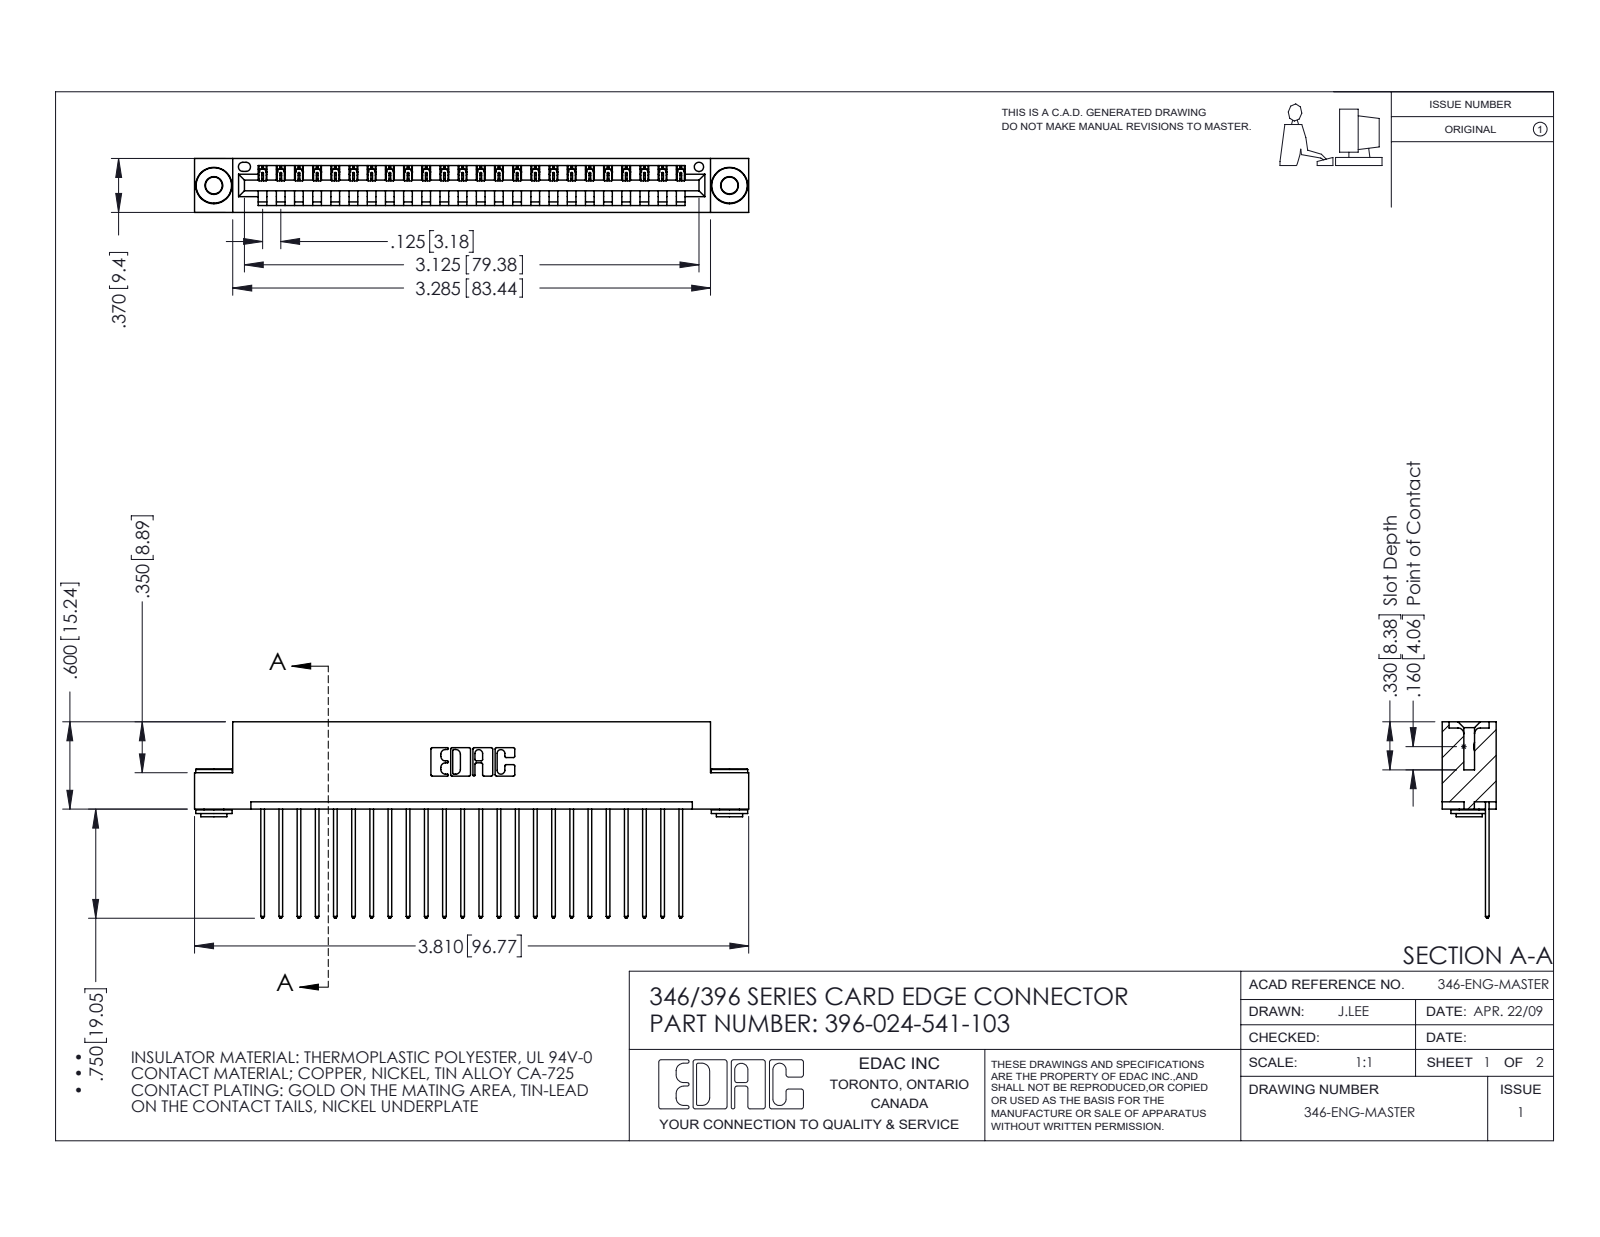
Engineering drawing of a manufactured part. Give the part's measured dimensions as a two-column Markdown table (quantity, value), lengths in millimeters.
| quantity | value |
| --- | --- |
| part name | 346 Part_Flush Mounting Lugs - 0.156 Dia-TH; 345-250-002_345-250-002-102; 396-024-541-103; 345-292-001_345-293-141 |
| STEP written by | SolidWorks 2016 (CONFIG_CONTROL_DESIGN) |
| units | millimeters |
| bodies | 27 solids, 1552 faces (1046 planar, 498 cylindrical, 8 other) |
| overall size | 96.8 × 34.3 × 9.4 |
| volume | 9 240 mm³ |
| surface area | 12 050 mm² |
| round holes (diameter × count) | 2.9 × 2, 4 × 2, 1.6 × 1 |
| round bosses / shafts (diameter × count) | 6.4 × 2, 4.6 × 2, 3.5 × 2 |
| partial cylindrical surfaces (radius × count) | 0.2 × 48, 0.3 × 48, 0.3 × 22, 0.2 × 6, 0.8 × 6, 0.7 × 3, 0.8 × 2, 1 × 2 |
| main face-to-face distances | 1.2, 8.2, 6.4, 9.4, 0.6, 1.8, 7.6, 3.8, 5.6, 2.5 |
| hole center spacings | 6.2, 84.8, 90 |
